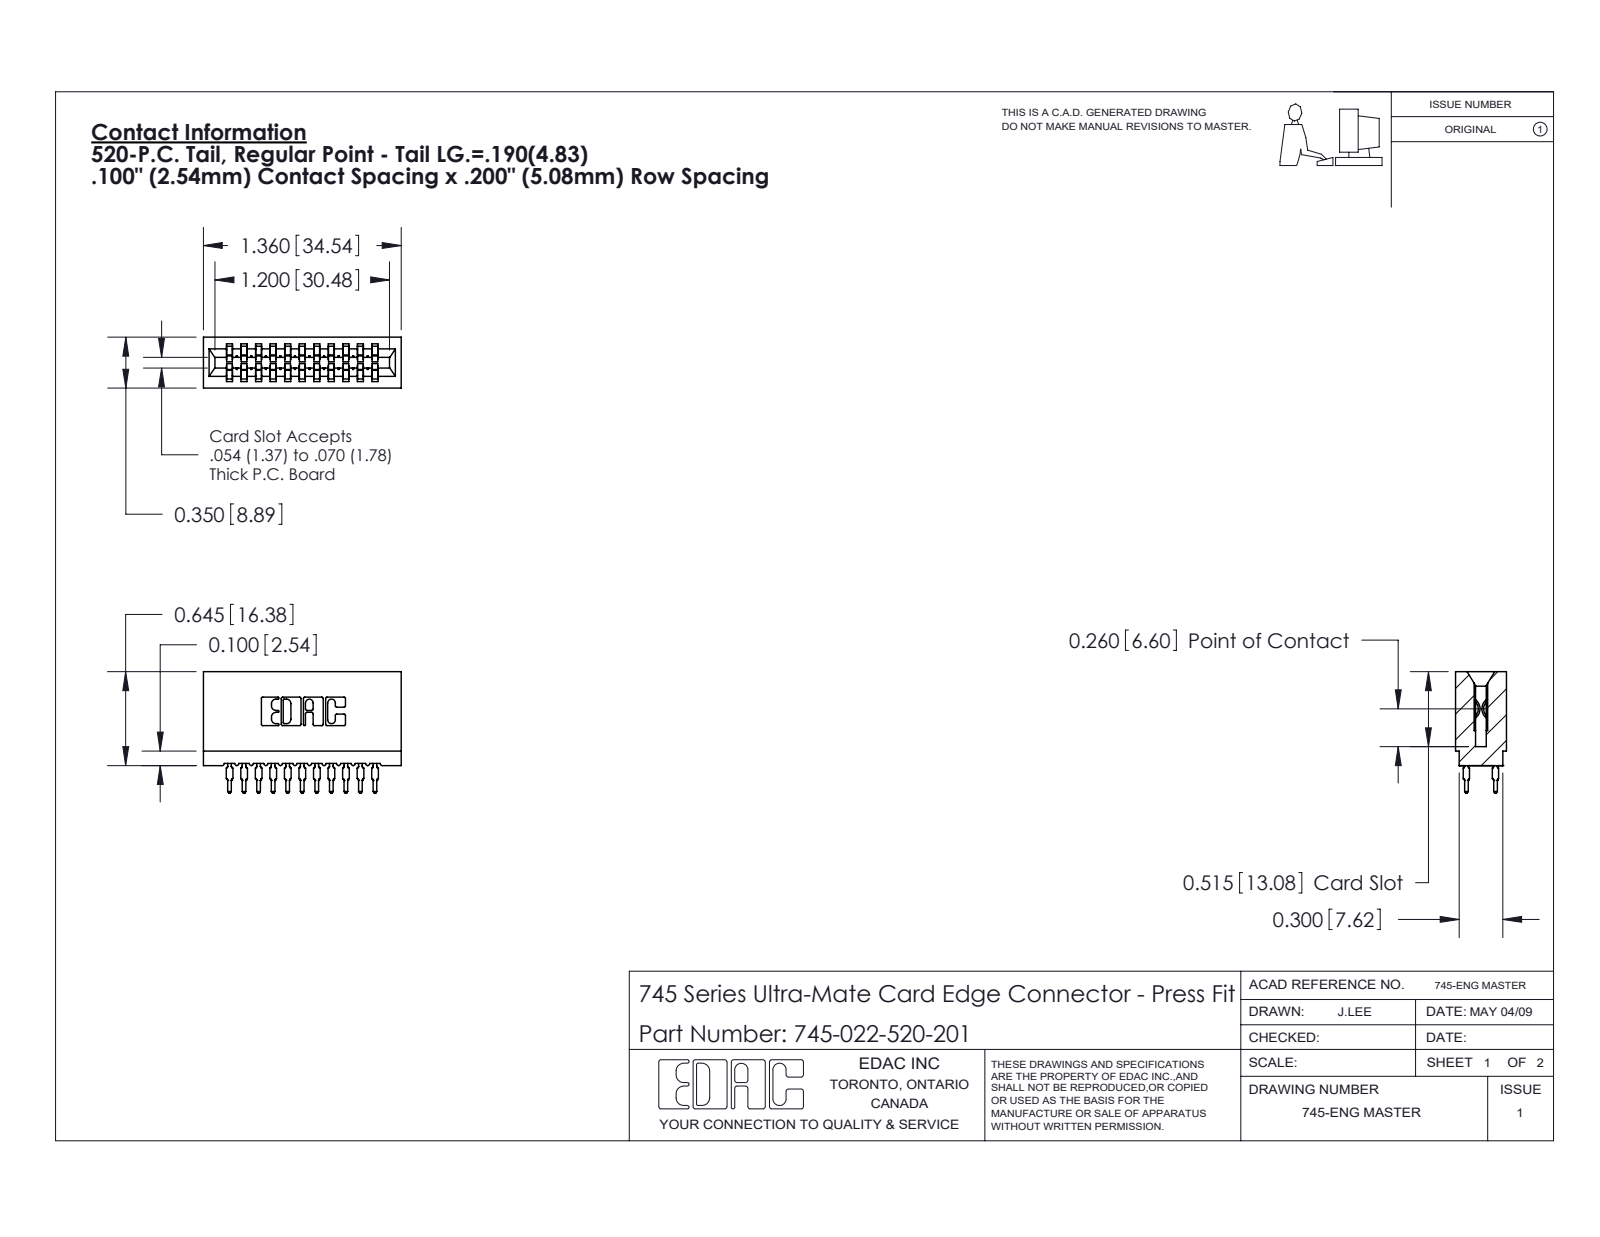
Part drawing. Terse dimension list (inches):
name: 745 Part_Insulator Option - 01; 745-292-001_520; 745-022-520-201
written by: SolidWorks 2020 (CONFIG_CONTROL_DESIGN)
unit: in
bodies: 23 solids, 2064 faces (1067 planar, 425 cylindrical, 572 other)
size: 1.36 × 0.836 × 0.35
volume: 0.2 in³; area: 9.066 in²
rounds: 44× R0.021, 22× R0.01, 22× R0.015, 8× R0.005, 8× R0.011, 6× R0.007, 6× R0.031, 3× R0.026
face distances: 0.2, 0.1, 0.3, 0.5, 0.4, 0.042, 0.35, 0.142, 0.6, 0.7
